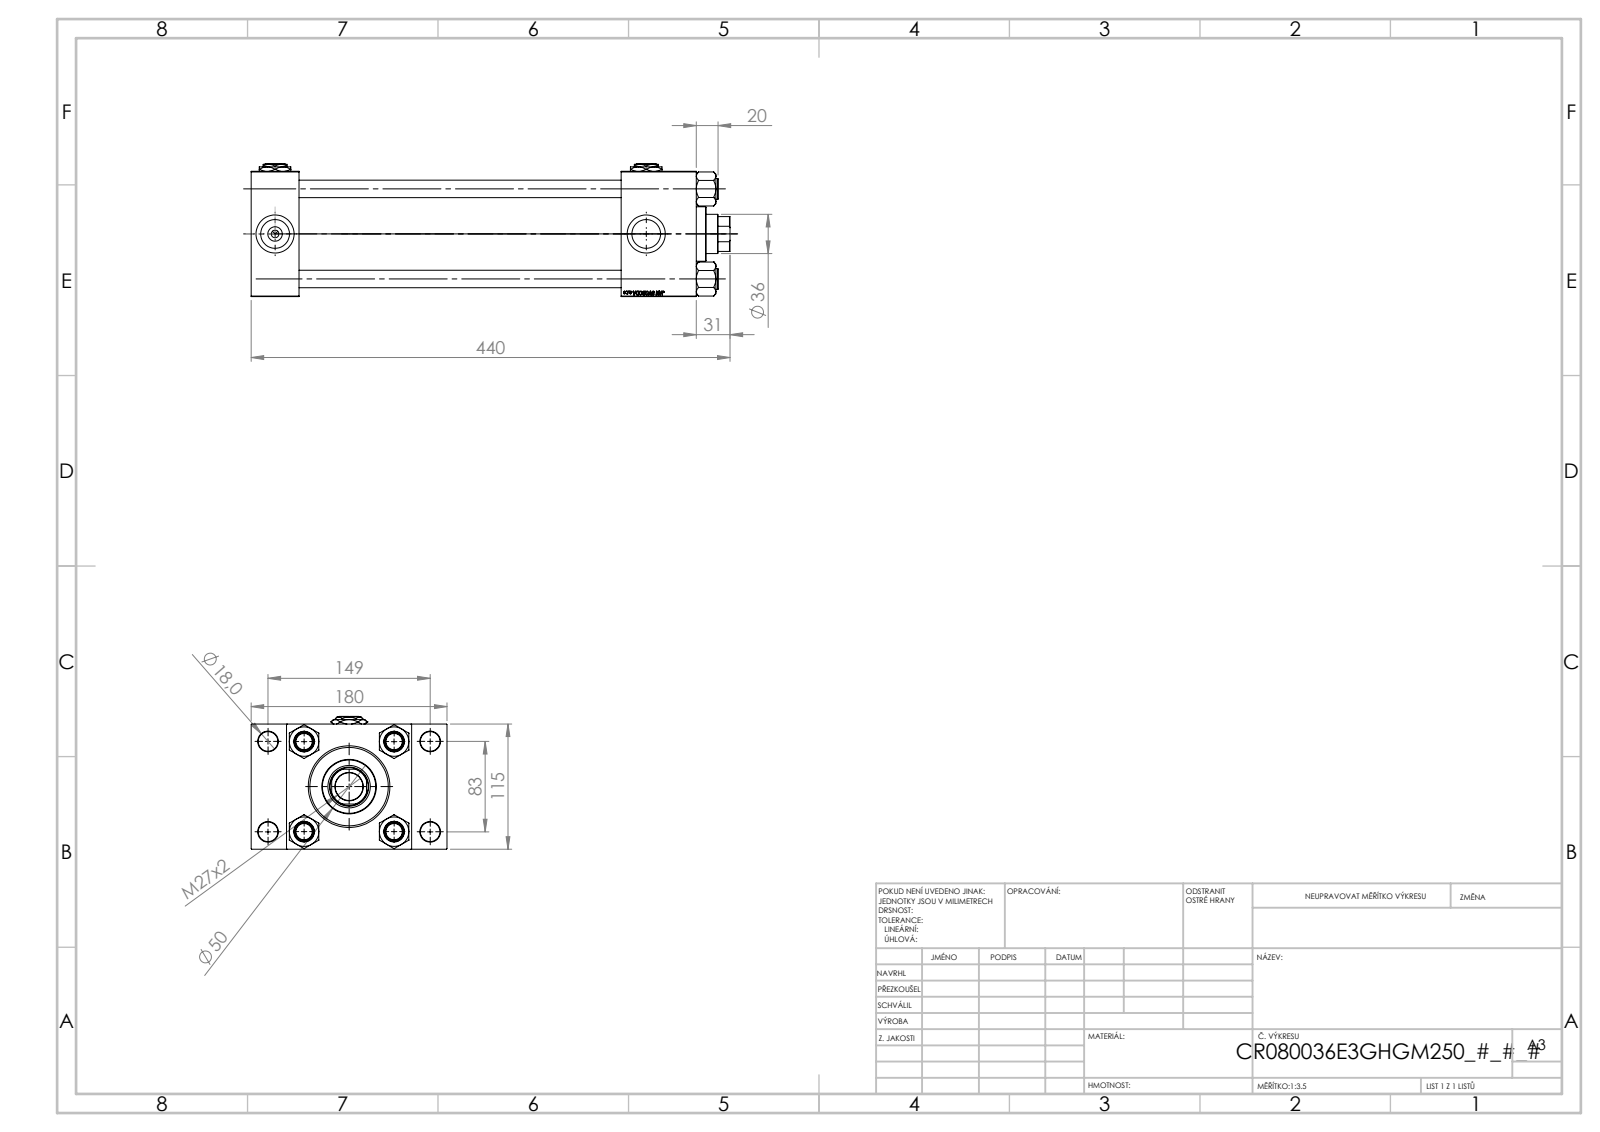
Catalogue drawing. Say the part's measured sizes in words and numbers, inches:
The part is named "V215CR_E_Body; Zatka_pro_OIL_PORT; V215CR_TYCINKA_E; NUT_M5_E (+2 more)". Its 3-D file was written by "SolidWorks 2019 (CONFIG_CONTROL_DESIGN)". It is 13 solids with 1290 faces: 595 planar, 101 cylindrical and 594 other. Overall it measures 17.323 by 7.087 by 4.803 inches. Its volume is 162.9 cubic inches and its surface area 789.9 square inches. Round holes: 4 of diameter 0.63, 4 of diameter 0.709, 4 of diameter 1.041, 4 of diameter 1.378, 3 of diameter 0.276, 2 of diameter 0.098, 1 of diameter 1.004, 1 of diameter 1.417, 1 of diameter 1.535, 1 of diameter 2.402, 1 of diameter 2.835, 1 of diameter 3.15. Round bosses or shafts: 4 of diameter 0.748, 1 of diameter 3.386, 1 of diameter 1.969. Partial cylindrical surfaces (rounded edges, fillets, slot ends): 1 of radius 0.689. The main face-to-face distances are 4.528, 1.732, 16.102, 14.37, 1.28, 5.807, 2.717, 13.386, 11.654, 14.972. The hole center spacings are 1.305, 1.652, 2.276, 2.302, 3.256, 3.357, 3.393, 3.513.
